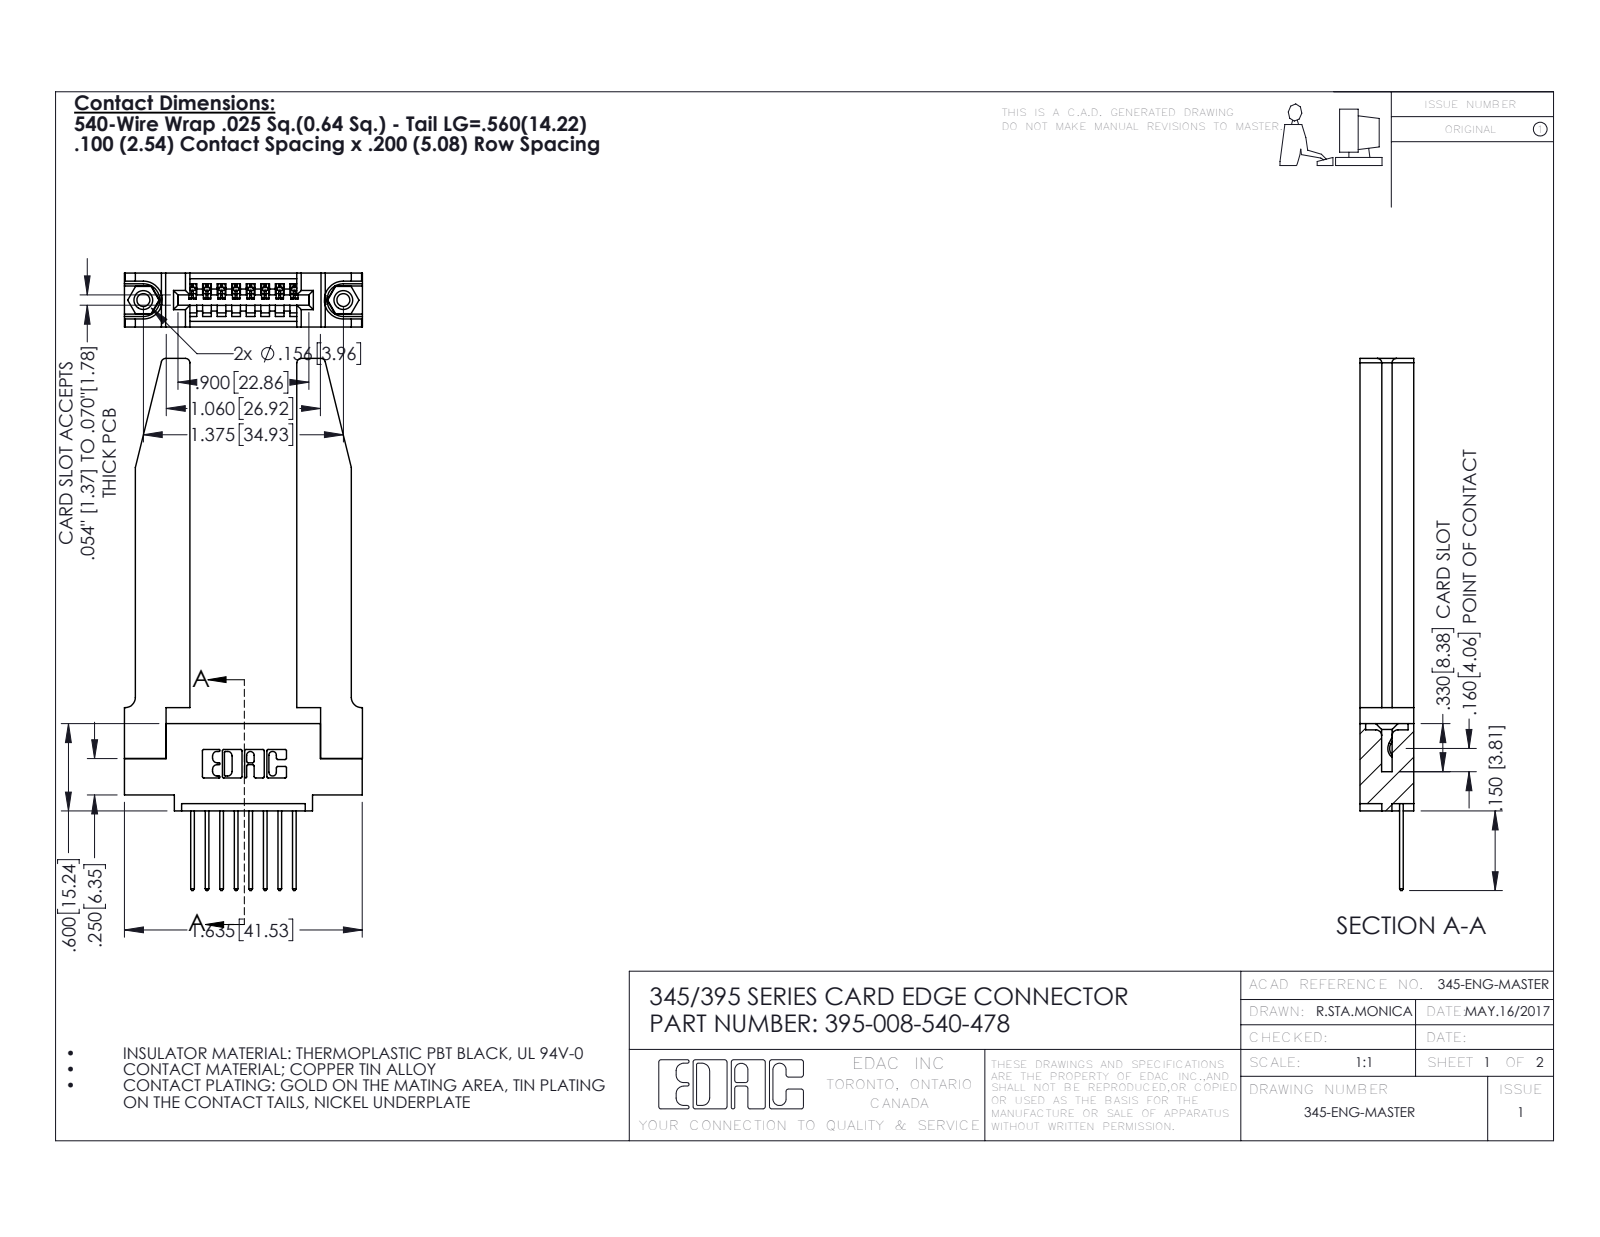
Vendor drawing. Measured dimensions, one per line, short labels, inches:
name: 345 Part_0.110 Offset - 0.156 Dia-TH; 345-292-001_345-293-140; 395-008-540-478; 345-250-001_345-250-001-102 (+1 more)
written by: SolidWorks 2016 (CONFIG_CONTROL_DESIGN)
unit: in
bodies: 13 solids, 828 faces (546 planar, 230 cylindrical, 52 other)
size: 3.657 × 1.636 × 0.37
volume: 0.694 in³; area: 17.57 in²
holes: 2× ⌀0.089, 2× ⌀0.125, 2× ⌀0.156, 1× ⌀0.064
bosses: 2× ⌀0.155
rounds: 22× R0.01, 16× R0.006, 16× R0.01, 8× R0.03, 6× R0.007, 6× R0.031, 3× R0.026, 2× R0.031
face distances: 0.37, 0.072, 0.15, 0.298, 0.22, 0.148, 0.735, 0.077, 0.098, 0.272
hole spacings: 0.27, 1.144, 1.375
